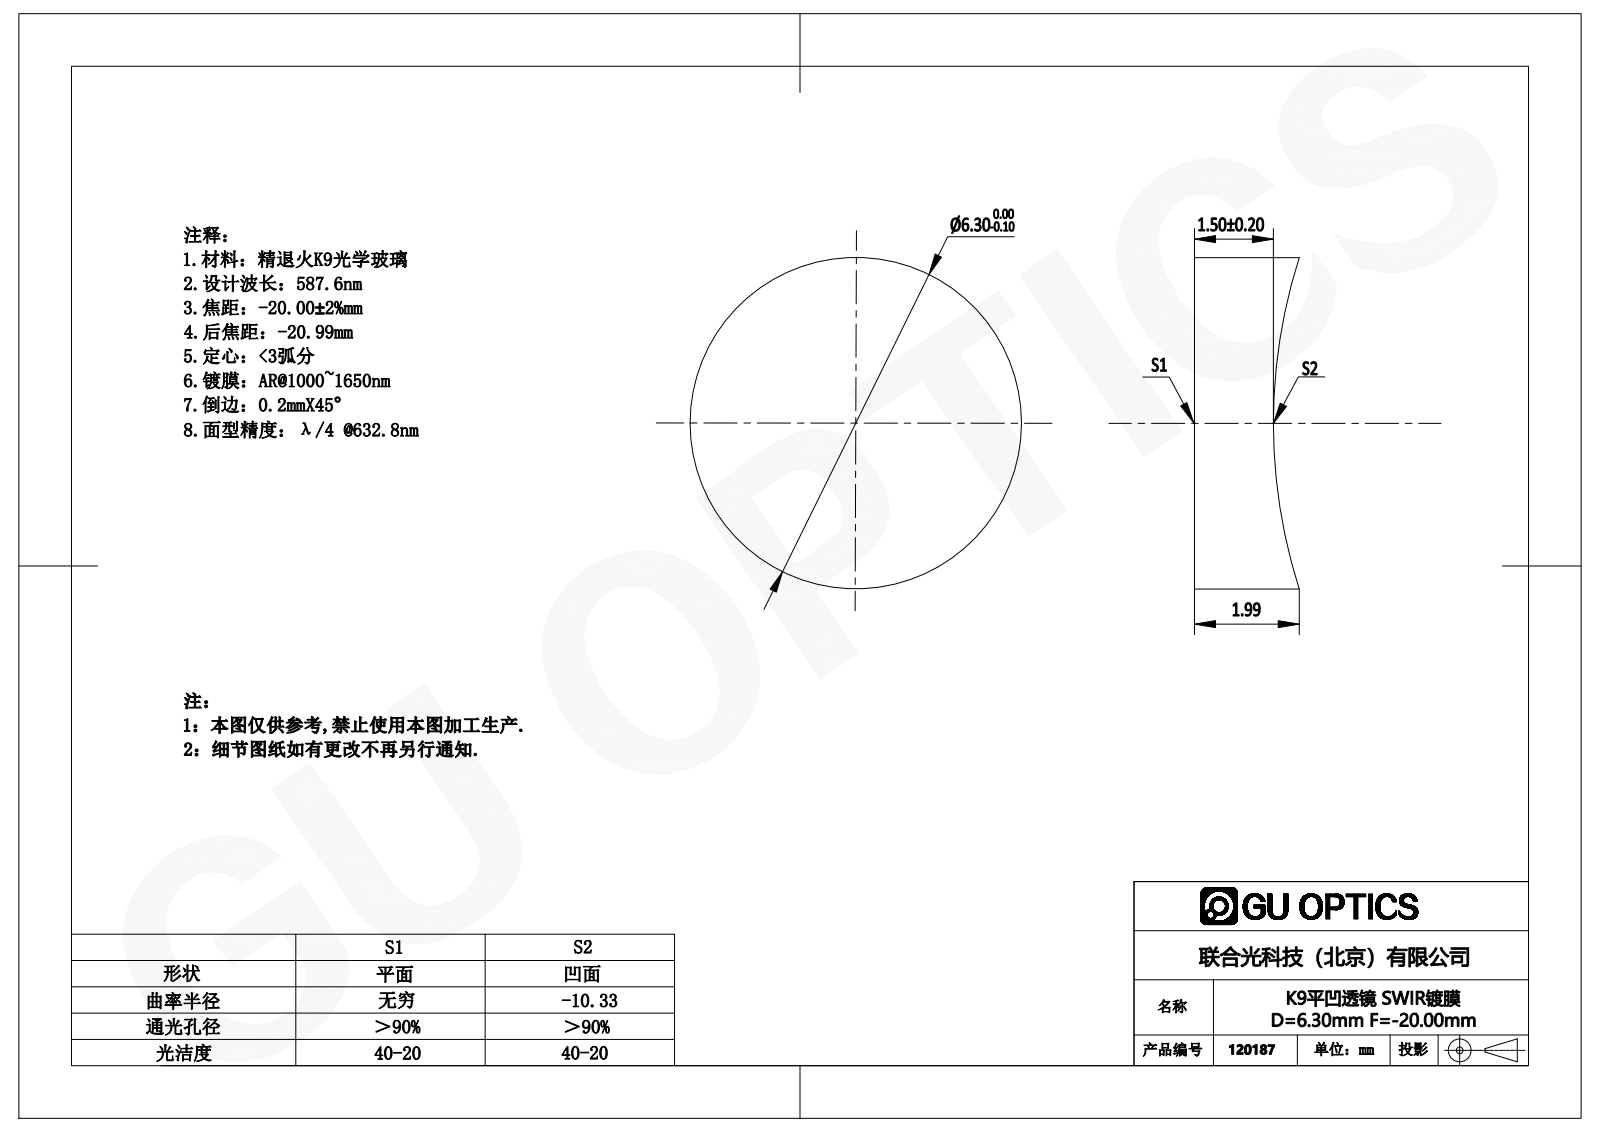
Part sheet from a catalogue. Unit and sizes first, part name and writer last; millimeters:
Units: millimetres
Overall size (bounding box): 6.3 × 6.3 × 1.99
Round bosses / shafts (diameter × count): ⌀6.3 ×1
Volume: 54 mm³ · Surface area: 103 mm²
Bodies: 1 solid, 5 faces (1 planar, 2 cylindrical, 2 other)
Part name (STEP PRODUCT): 120127
STEP written by: SolidWorks 2016 (AUTOMOTIVE_DESIGN)
